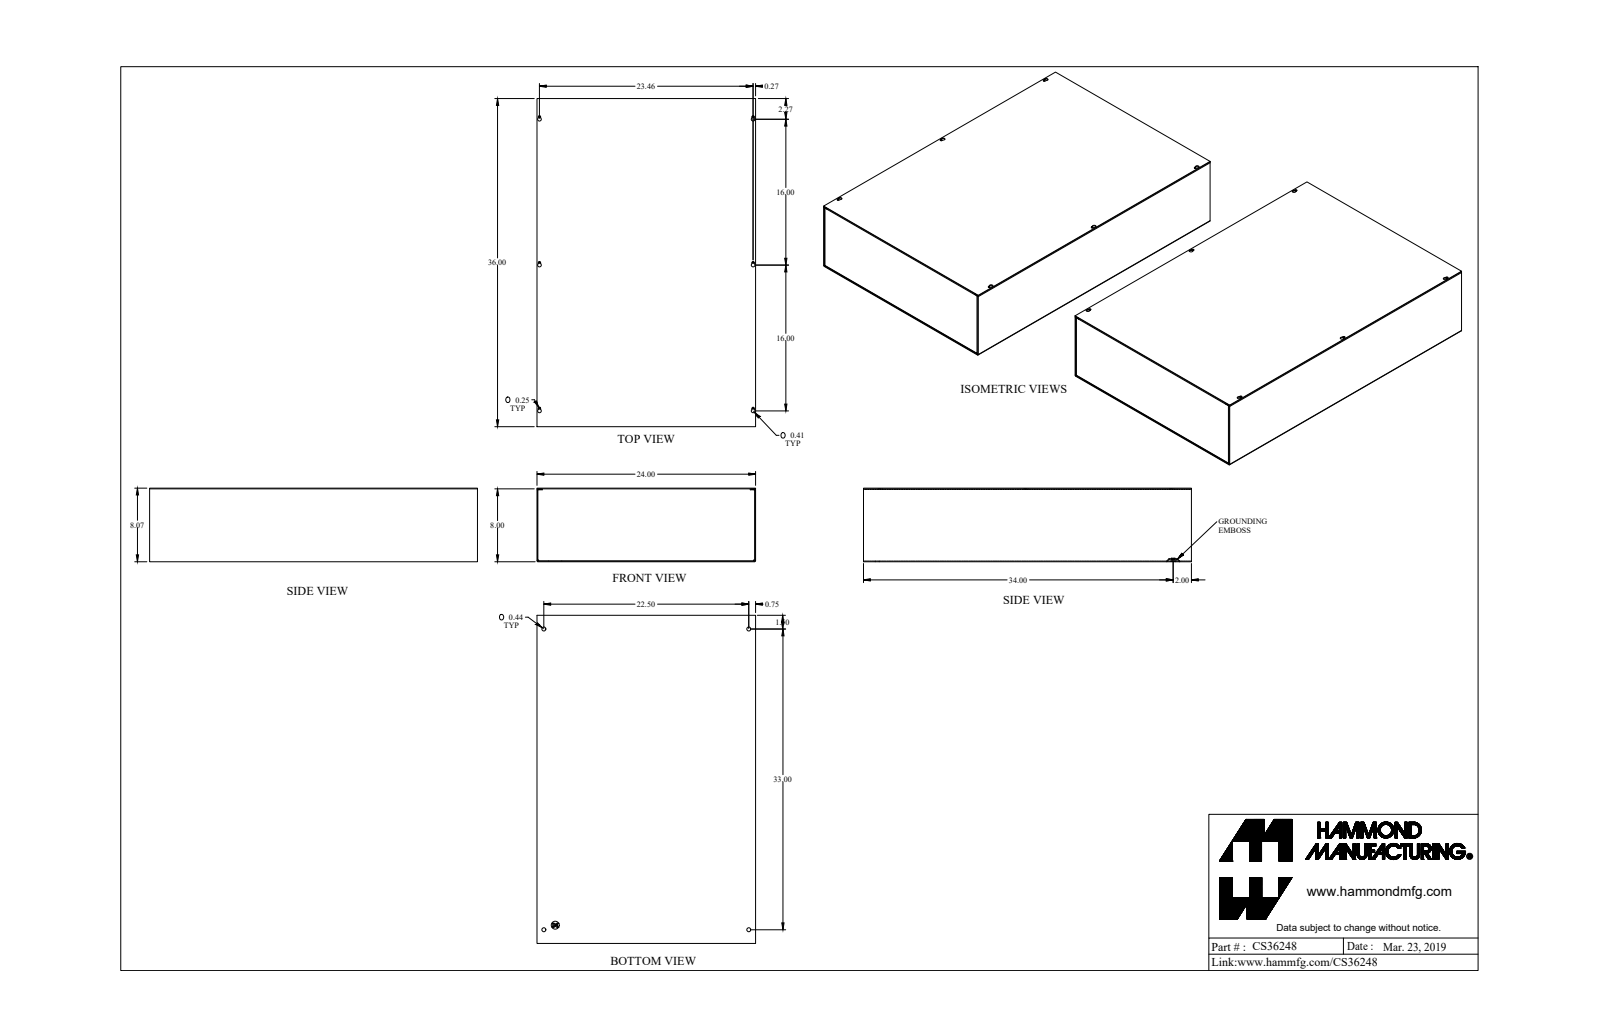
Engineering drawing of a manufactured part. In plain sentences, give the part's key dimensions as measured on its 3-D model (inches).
The part is named "CS36248_Default". Its 3-D file was written by "SolidWorks 2019 (CONFIG_CONTROL_DESIGN)". It is 4 solids with 221 faces: 129 planar, 84 cylindrical and 8 other. Overall it measures 36 by 24 by 8.072 inches. Its volume is 198.7 cubic inches and its surface area 5 551 square inches. Round holes: 7 of diameter 0.17, 4 of diameter 0.437, 1 of diameter 0.5. Round bosses or shafts: 1 of diameter 0.492, 1 of diameter 0.314. Partial cylindrical surfaces (rounded edges, fillets, slot ends): 12 of radius 0.036, 12 of radius 0.108, 8 of radius 0.072, 6 of radius 0.125, 6 of radius 0.203. The main face-to-face distances are 0.072, 8, 7.928, 8.072, 23.928, 35.928, 24, 23.856, 36, 35.856. The hole center spacings are 0.693, 16, 16.507, 22.985, 28.29, 28.396, 32.504, 39.804.
